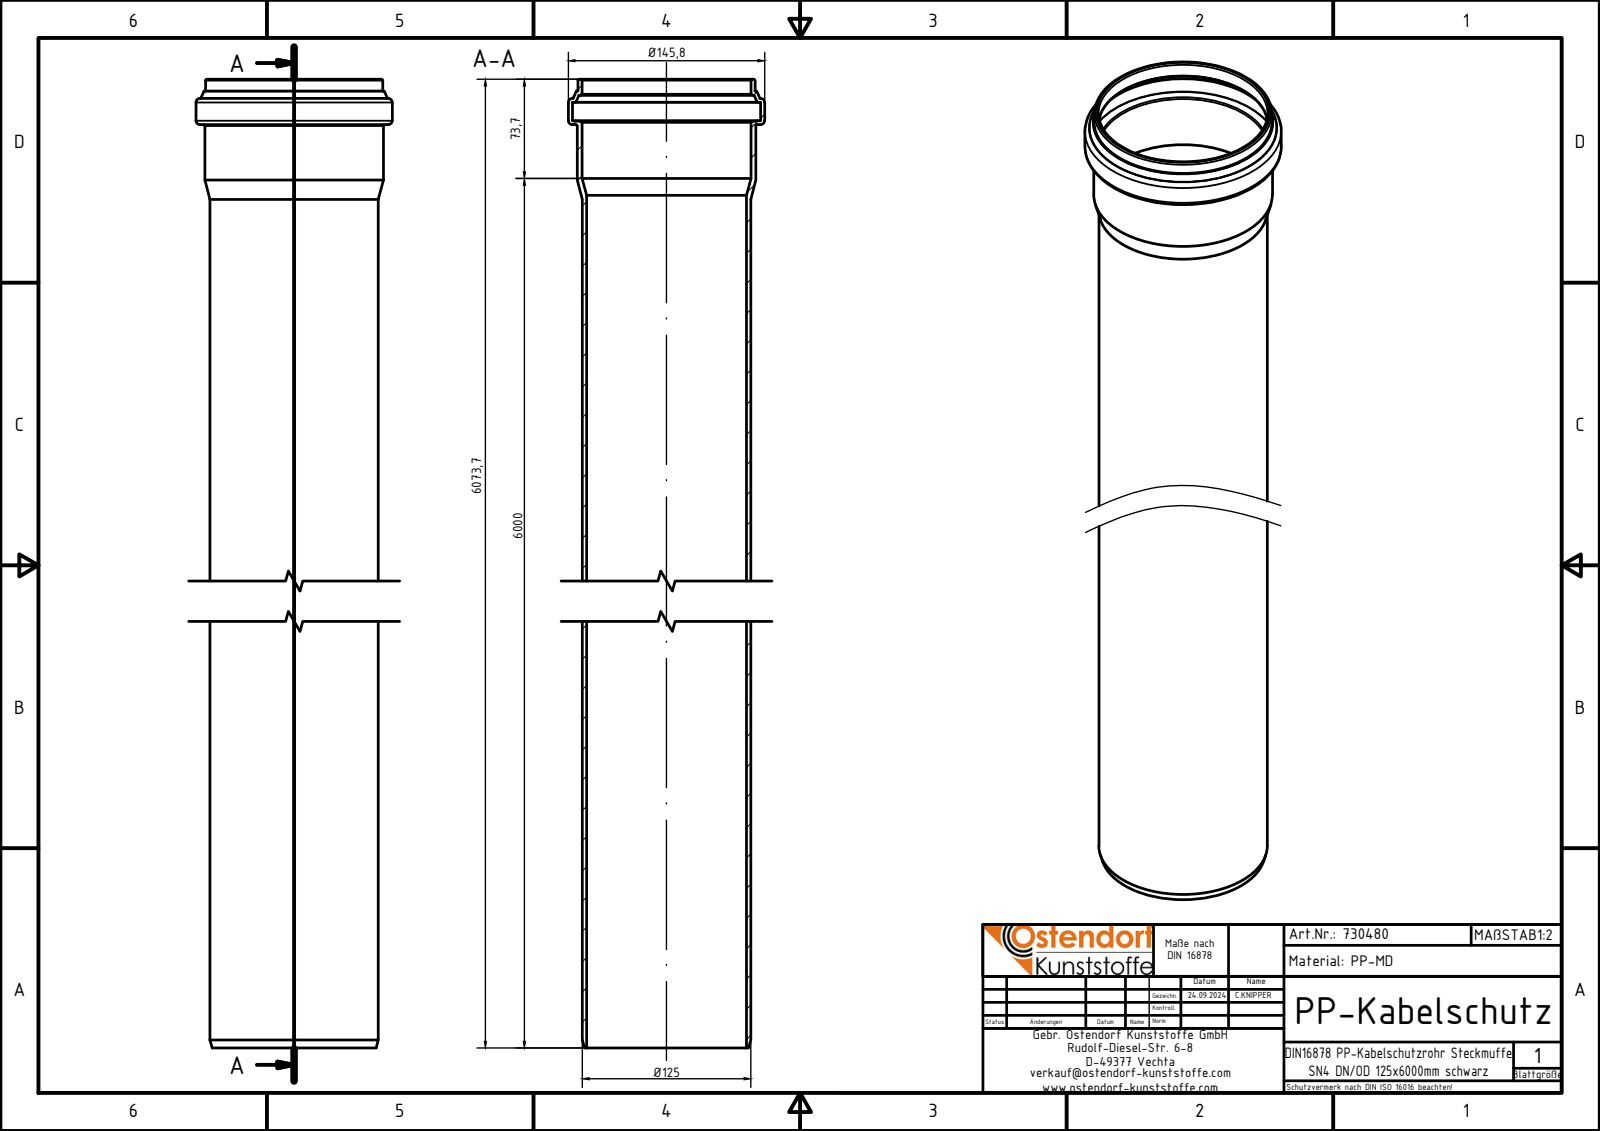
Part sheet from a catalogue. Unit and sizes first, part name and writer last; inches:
Units: inches
Overall size (bounding box): 239.122 × 5.74 × 5.74
Round holes (diameter × count): ⌀4.677 ×1, ⌀4.941 ×1, ⌀5.504 ×1
Round bosses / shafts (diameter × count): ⌀5.74 ×1, ⌀5.224 ×1, ⌀5.177 ×1, ⌀4.921 ×1
Main face-to-face distances: 237.795, 239.122, 1.327, 238.774, 0.979, 0.348, 238.563, 0.768, 0.211, 0.559
Volume: 441.9 in³ · Surface area: 7 234 in²
Bodies: 1 solid, 35 faces (5 planar, 8 cylindrical, 22 other)
Part name (STEP PRODUCT): 730480z
STEP written by: Autodesk Inventor 2024 (AUTOMOTIVE_DESIGN)
